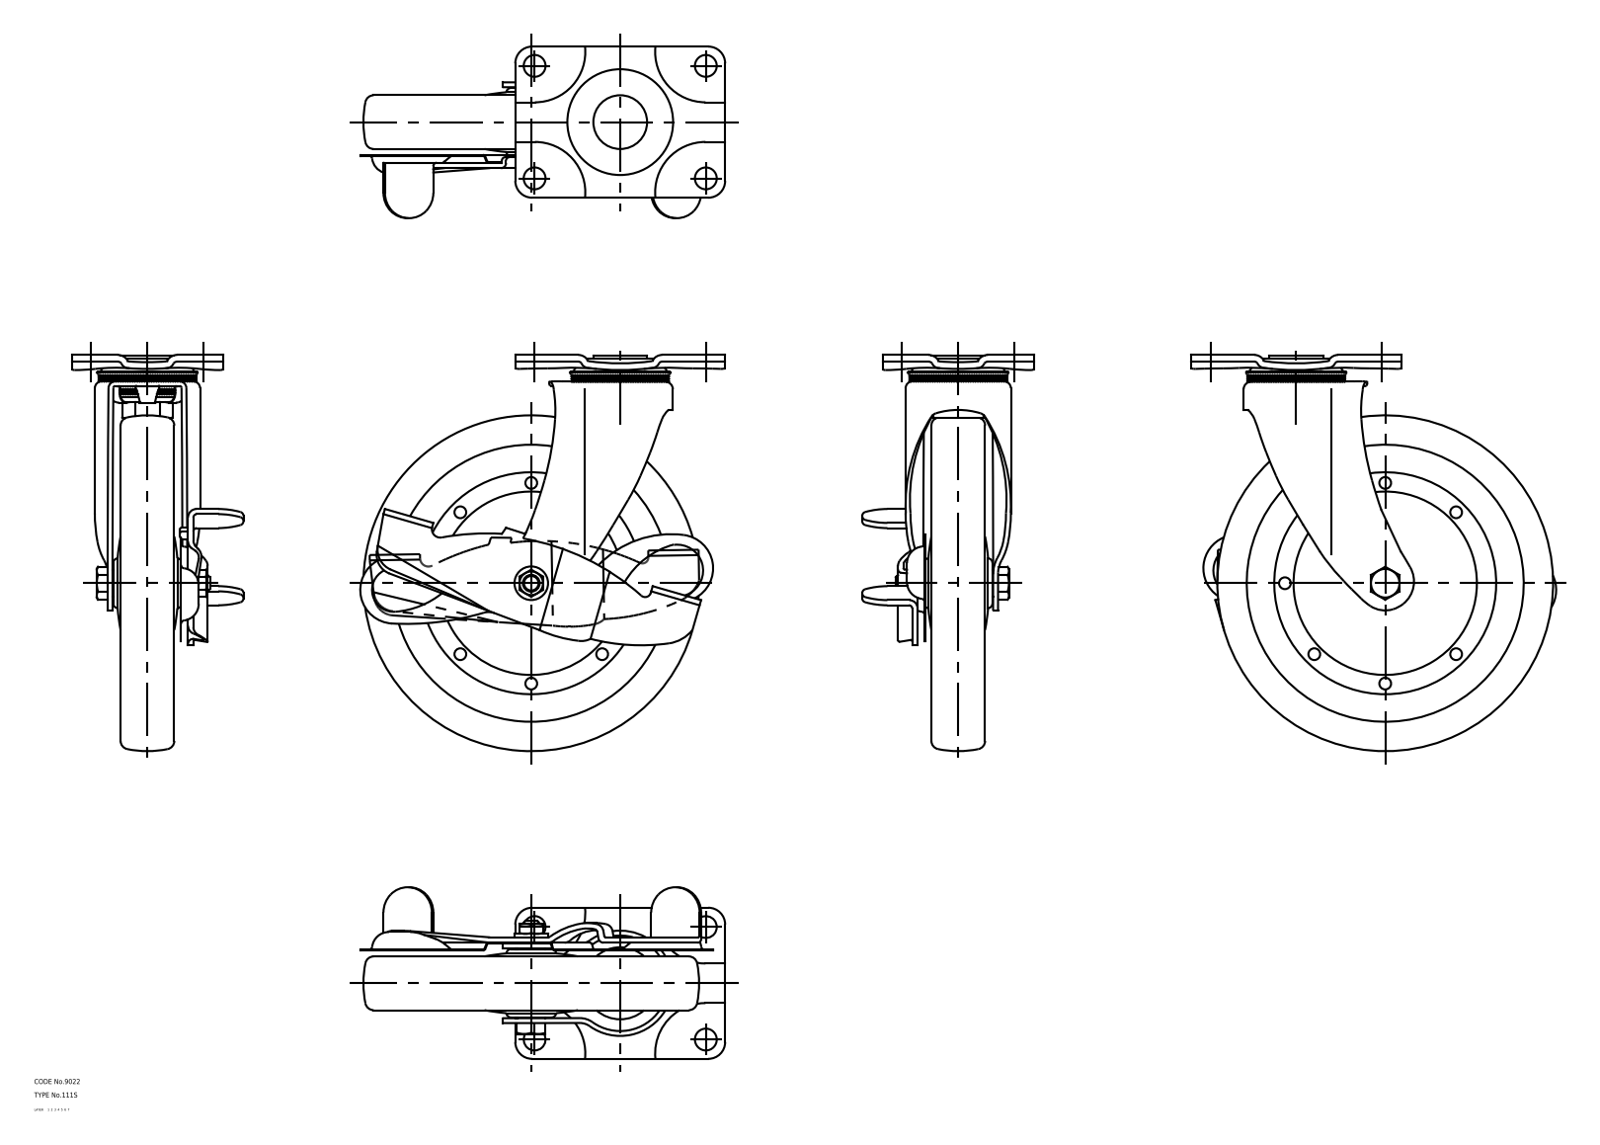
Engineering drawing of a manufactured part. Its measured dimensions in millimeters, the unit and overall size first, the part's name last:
Units: millimetres
Overall size (bounding box): 236 × 217.36 × 102.2
Volume: 1 053 000 mm³ · Surface area: 198 910 mm²
Bodies: 7 solids, 624 faces (0 planar, 0 cylindrical, 624 other)
Part name (STEP PRODUCT): 67155578; 67155591; 67155604; 67155617 (+3 more)
STEP written by: CADfix (AUTOMOTIVE_DESIGN)
